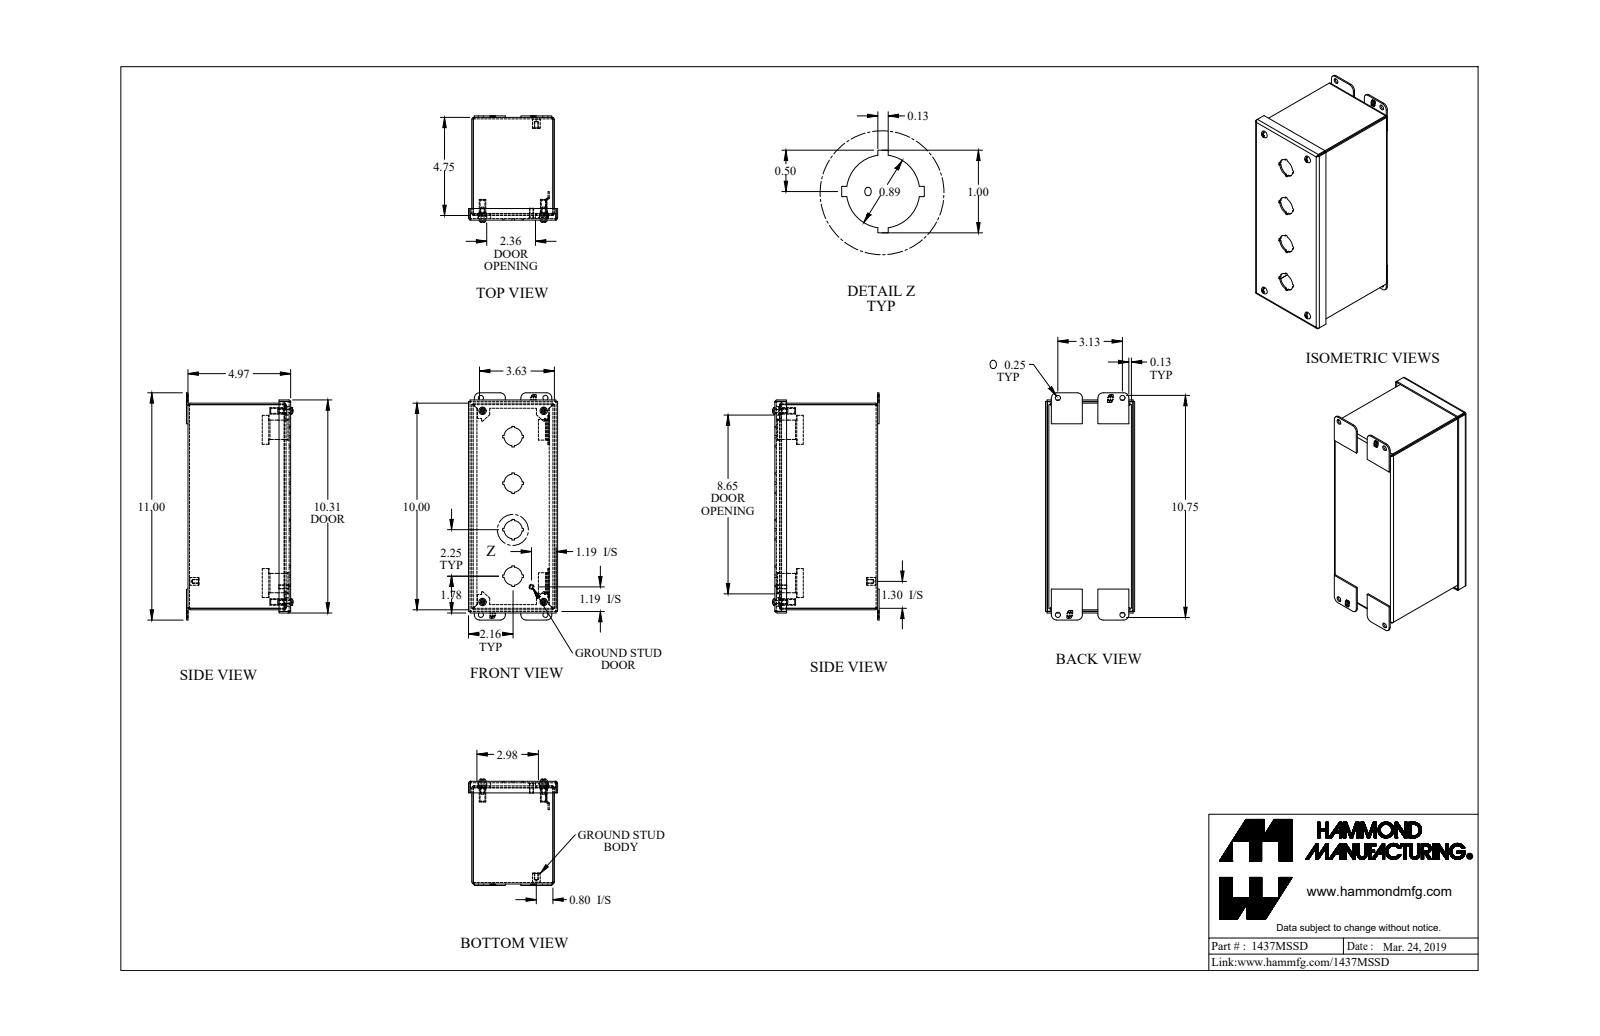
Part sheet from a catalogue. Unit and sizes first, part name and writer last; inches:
Units: inches
Overall size (bounding box): 11 × 5.154 × 4.312
Round holes (diameter × count): ⌀0.25 ×8, ⌀0.065 ×4, ⌀0.239 ×4, ⌀0.253 ×4, ⌀0.406 ×4, ⌀0.886 ×4, ⌀0.156 ×1
Round bosses / shafts (diameter × count): ⌀0.19 ×5, ⌀0.406 ×4, ⌀0.315 ×4, ⌀0.148 ×4, ⌀0.375 ×1, ⌀0.25 ×1
Partial cylindrical surfaces — rounded edges, fillets, slot ends (radius × count): R0.036 ×12, R0.108 ×12, R0.25 ×8, R0.029 ×4, R0.086 ×4, R0.171 ×4, R0.125 ×2
Main face-to-face distances: 0.072, 3.928, 4.9, 4.972, 3.856, 4, 4.828, 9.928, 0.156, 4.084
Hole centre spacings: 9.25, 9.875, 10.333, 2.961, 3.107, 9.712, 2.962, 0.63
Volume: 20.14 in³ · Surface area: 537.8 in²
Bodies: 23 solids, 669 faces (471 planar, 168 cylindrical, 30 other)
Part name (STEP PRODUCT): 1437MSSD_Default
STEP written by: SolidWorks 2019 (CONFIG_CONTROL_DESIGN)
